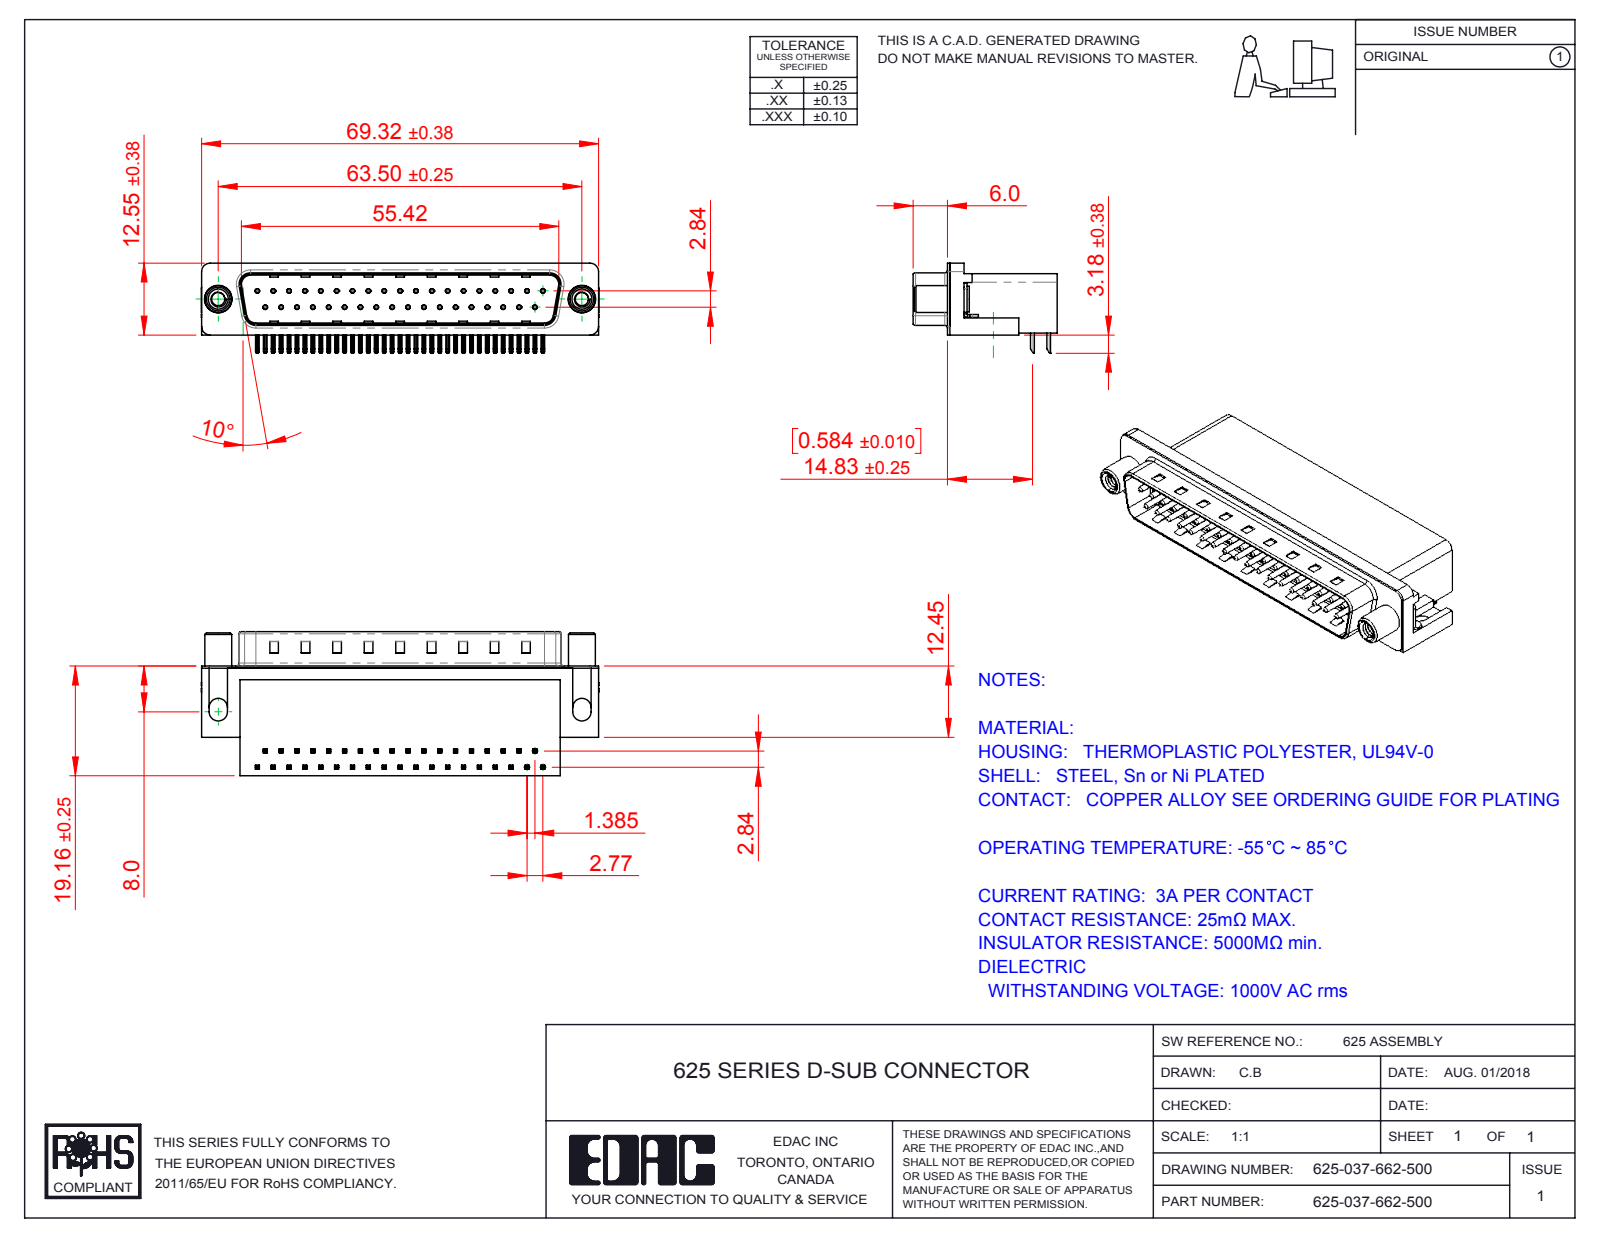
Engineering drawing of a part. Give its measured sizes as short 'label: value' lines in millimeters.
name: 625 Contact Top; 625 Housing_37 Socket; 625 Shell_37 Socket; 625 Non Board Mount (+3 more)
written by: SolidWorks 2016 (CONFIG_CONTROL_DESIGN)
unit: mm
bodies: 43 solids, 3193 faces (2007 planar, 921 cylindrical, 265 other)
size: 69.4 × 25.16 × 15.73
volume: 12 663 mm³; area: 11 819 mm²
holes: 37× ⌀0.35, 37× ⌀0.8, 2× ⌀2.3, 2× ⌀3.1, 2× ⌀4, 2× ⌀4.8, 2× ⌀5
bosses: 37× ⌀0.75, 2× ⌀4.9, 2× ⌀4.7, 2× ⌀4.5, 2× ⌀3.85
rounds: 148× R0.25, 74× R0.12, 16× R1, 9× R0.5, 8× R1.6, 7× R1.5, 4× R0.9, 4× R2
face distances: 10.34, 0.4, 18.76, 8.76, 2.84, 19.16, 2.09, 10.1, 1.74, 8.36
hole spacings: 3.16, 2.77, 5.54, 8.31, 11.08, 13.85, 19.39, 22.16
